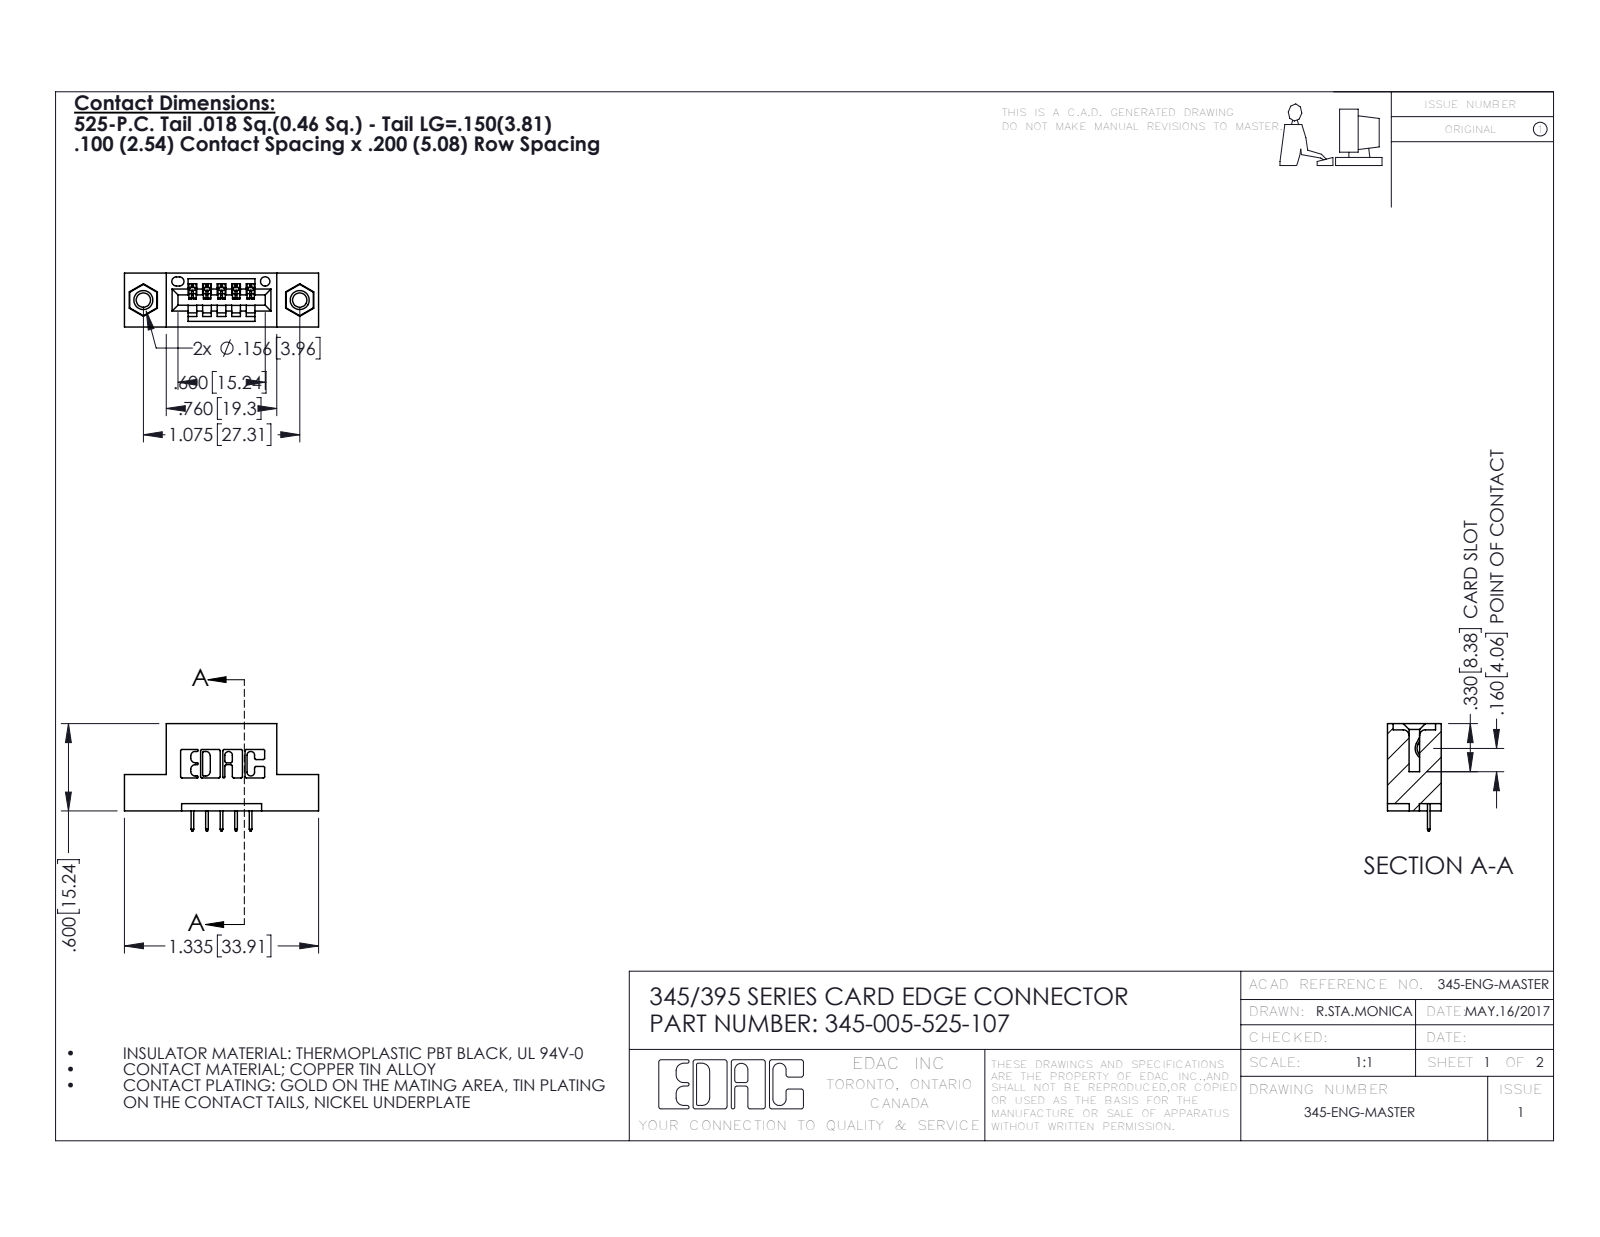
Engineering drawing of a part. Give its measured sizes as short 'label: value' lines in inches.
name: 345-250-001_345-250-005-103; 345-292-001_345-293-125; 345 Part_Flush Mounting Lugs - 0.156 Dia-TI; 345-005-525-107
written by: SolidWorks 2020 (CONFIG_CONTROL_DESIGN)
unit: in
bodies: 8 solids, 496 faces (342 planar, 138 cylindrical, 16 other)
size: 1.335 × 0.737 × 0.37
volume: 0.176 in³; area: 5.105 in²
holes: 2× ⌀0.098, 2× ⌀0.125, 2× ⌀0.156, 1× ⌀0.064
bosses: 2× ⌀0.155
rounds: 22× R0.01, 10× R0.006, 6× R0.007, 6× R0.031, 3× R0.026, 2× R0.031, 2× R0.04, 1× R0.014
face distances: 0.2, 0.37, 0.1, 0.072, 0.298, 0.35, 0.25, 0.06, 0.55, 0.025
hole spacings: 0.27, 0.847, 1.075
